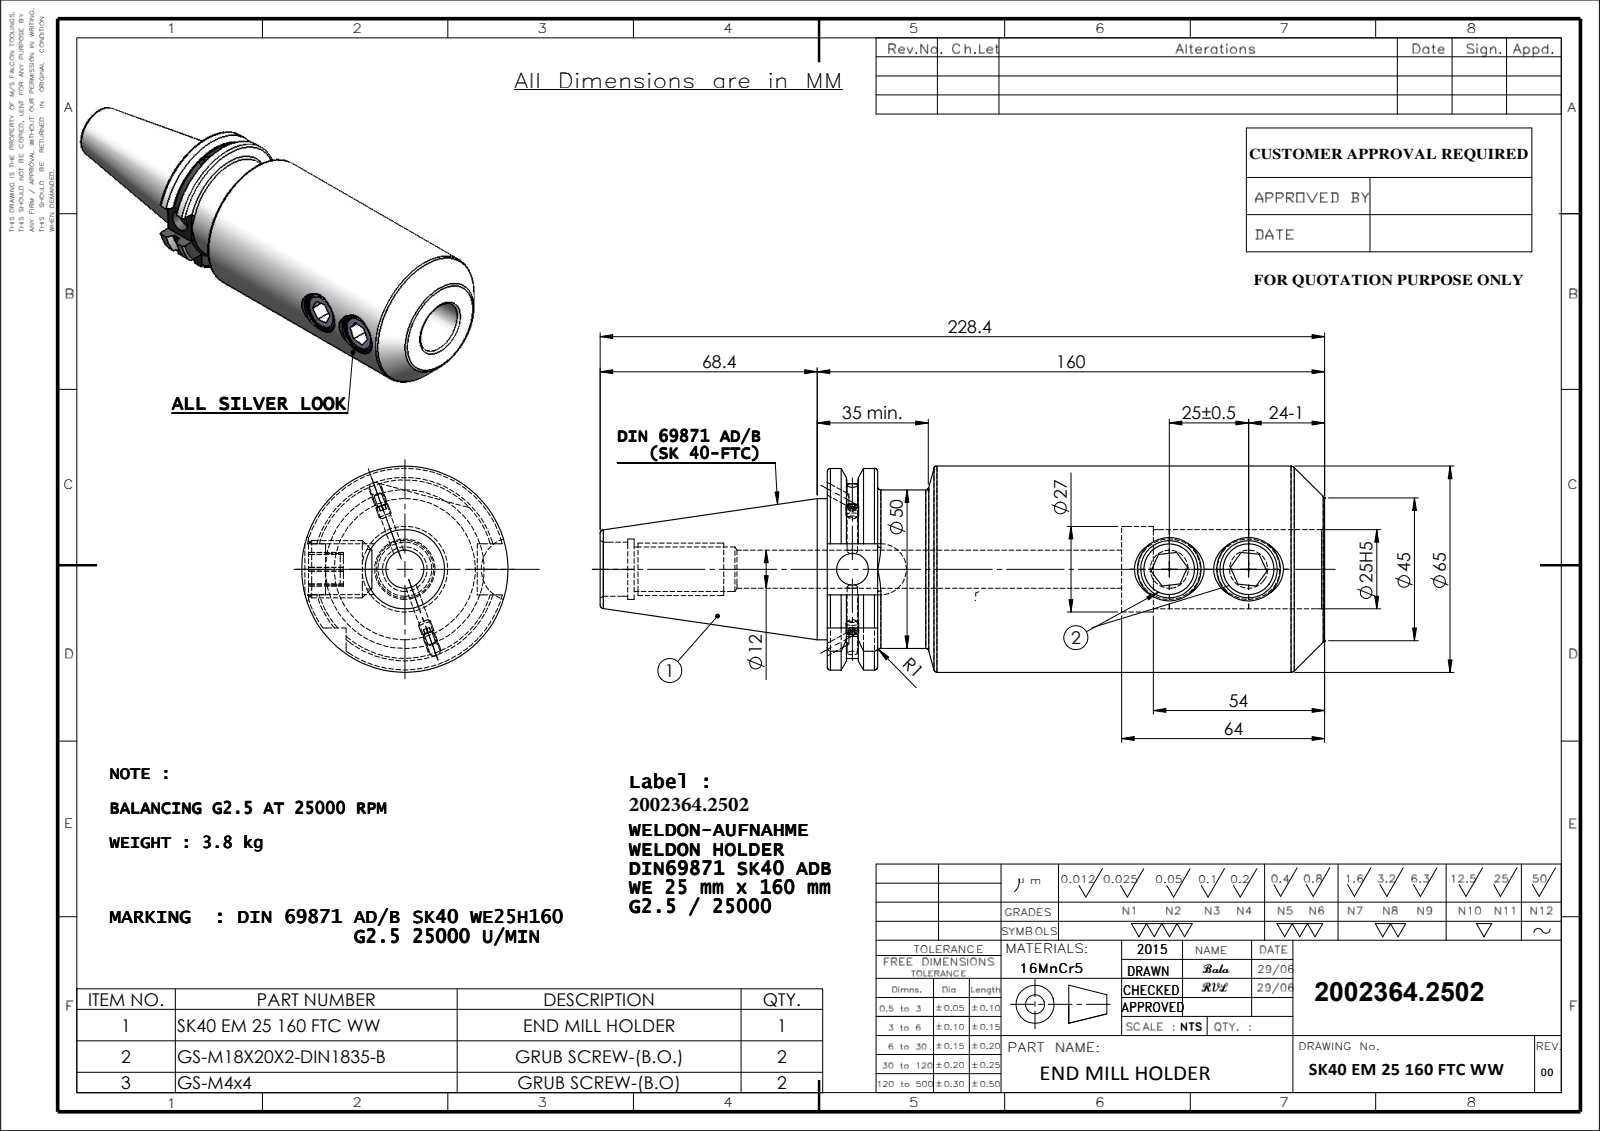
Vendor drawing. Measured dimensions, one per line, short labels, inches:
name: Copy of M4X4_DIN 913 - M4 x 4-N; GS-M18X2X20; 91406-WE725160; SK40 EM 25 160 FTC WW
written by: SolidWorks 2009 (CONFIG_CONTROL_DESIGN)
unit: in
bodies: 5 solids, 197 faces (69 planar, 53 cylindrical, 75 other)
size: 8.992 × 2.559 × 2.559
volume: 29.94 in³; area: 98.52 in²
holes: 2× ⌀0.63, 2× ⌀0.787, 1× ⌀0.13, 1× ⌀0.394, 1× ⌀0.472, 1× ⌀0.551, 1× ⌀0.669, 1× ⌀0.748, 1× ⌀0.984, 1× ⌀1.063
bosses: 2× ⌀0.709, 2× ⌀0.157, 1× ⌀2.559, 1× ⌀1.969, 1× ⌀1.75
rounds: 1× R0.317, 1× R1.107, 1× R1.251
face distances: 6.173, 0.626, 5.547, 0.394, 3.654, 3.028, 2.52, 2.094, 0.787, 1.307
hole spacings: 0.984, 3.931, 4.915
